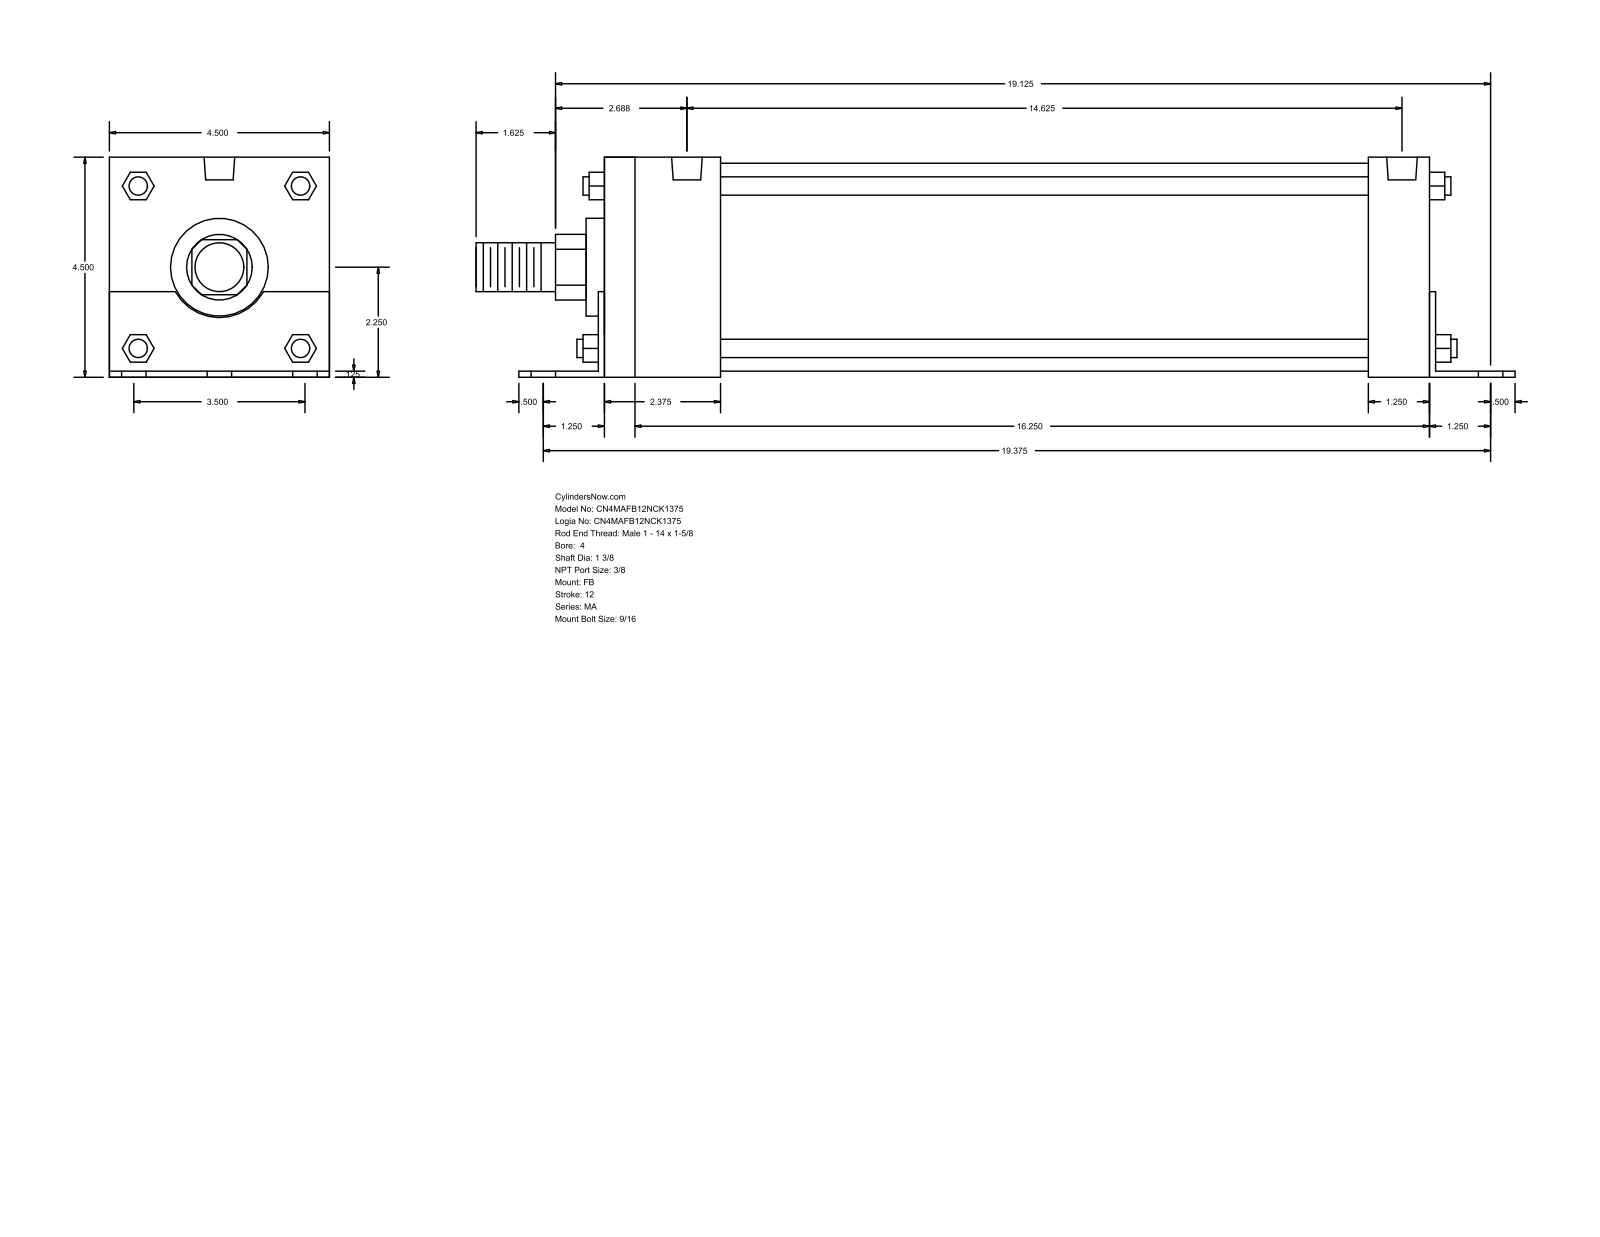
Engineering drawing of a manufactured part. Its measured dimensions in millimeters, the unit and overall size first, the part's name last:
Units: millimetres
Overall size (bounding box): 539.75 × 114.35 × 114.3
Round holes (diameter × count): ⌀14.29 ×6, ⌀11.11 ×4, ⌀15.93 ×2
Round bosses / shafts (diameter × count): ⌀9.53 ×4, ⌀107.95 ×1, ⌀50.8 ×1, ⌀34.92 ×1, ⌀25.4 ×1
Partial cylindrical surfaces — rounded edges, fillets, slot ends (radius × count): R17.06 ×1, R26.16 ×1
Main face-to-face distances: 114.3, 3.17, 114.35, 3.12, 111.18, 428.62, 3.18, 431.8, 34.93, 431.79
Hole centre spacings: 44.45, 494.12, 492.12, 63.99, 67.49, 86.85, 88.9, 90.98
Bodies: 0 solids, 140 faces (105 planar, 35 cylindrical, 0 other)
Part name (STEP PRODUCT): MA_FB__0400_1.375
STEP written by: GSSL Pune (CONFIG_CONTROL_DESIGN)
